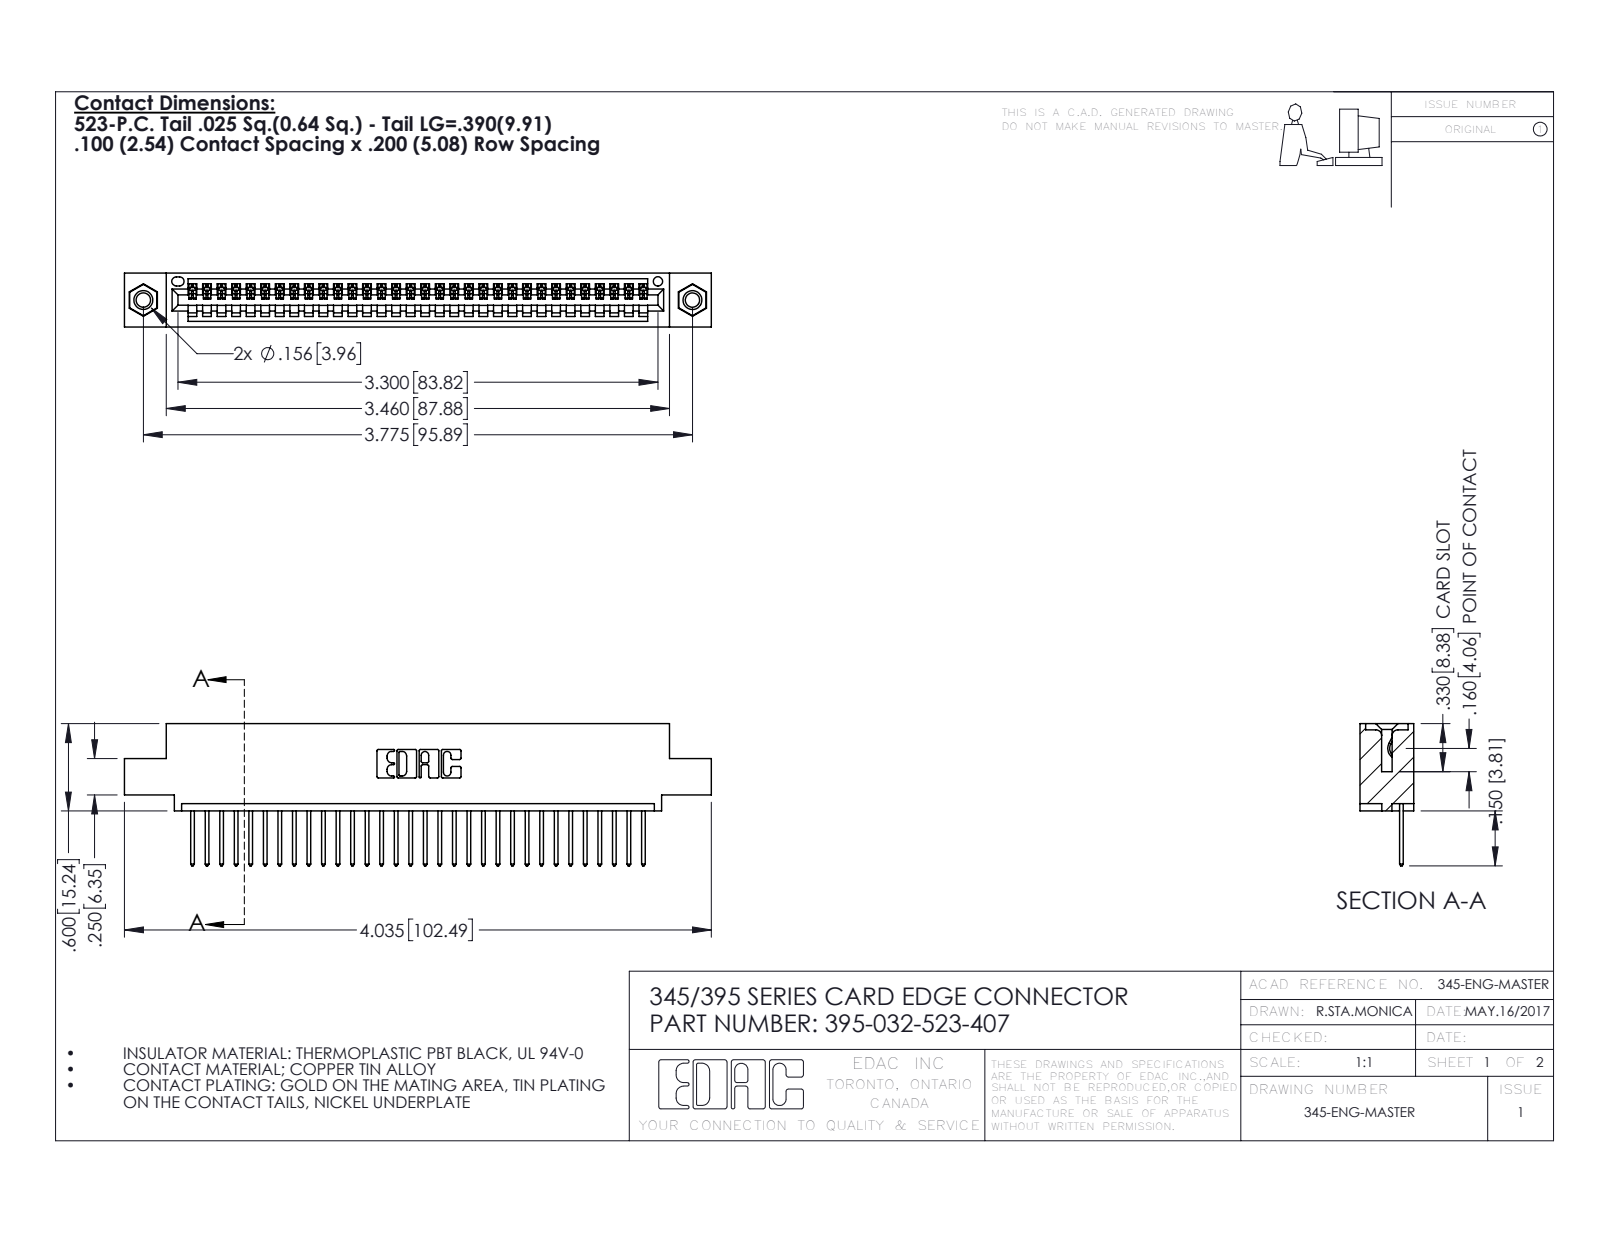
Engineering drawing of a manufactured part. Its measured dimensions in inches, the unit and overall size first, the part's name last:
Units: inches
Overall size (bounding box): 4.035 × 0.977 × 0.37
Round holes (diameter × count): ⌀0.098 ×2, ⌀0.125 ×2, ⌀0.156 ×2, ⌀0.064 ×1
Round bosses / shafts (diameter × count): ⌀0.155 ×2
Partial cylindrical surfaces — rounded edges, fillets, slot ends (radius × count): R0.006 ×64, R0.01 ×64, R0.01 ×22, R0.007 ×6, R0.031 ×6, R0.026 ×3, R0.031 ×2, R0.04 ×2
Main face-to-face distances: 0.072, 0.298, 0.37, 0.2, 0.098, 0.272, 0.025, 0.225, 0.149, 0.072
Hole centre spacings: 0.27, 3.54, 3.775
Volume: 0.583 in³ · Surface area: 19.7 in²
Bodies: 35 solids, 2046 faces (1396 planar, 634 cylindrical, 16 other)
Part name (STEP PRODUCT): 345-292-001_345-293-123; 345 Part_0.110 Offset - 0.156 Dia-TI; 345-250-001_345-250-005-103; 395-032-523-407
STEP written by: SolidWorks 2016 (CONFIG_CONTROL_DESIGN)
